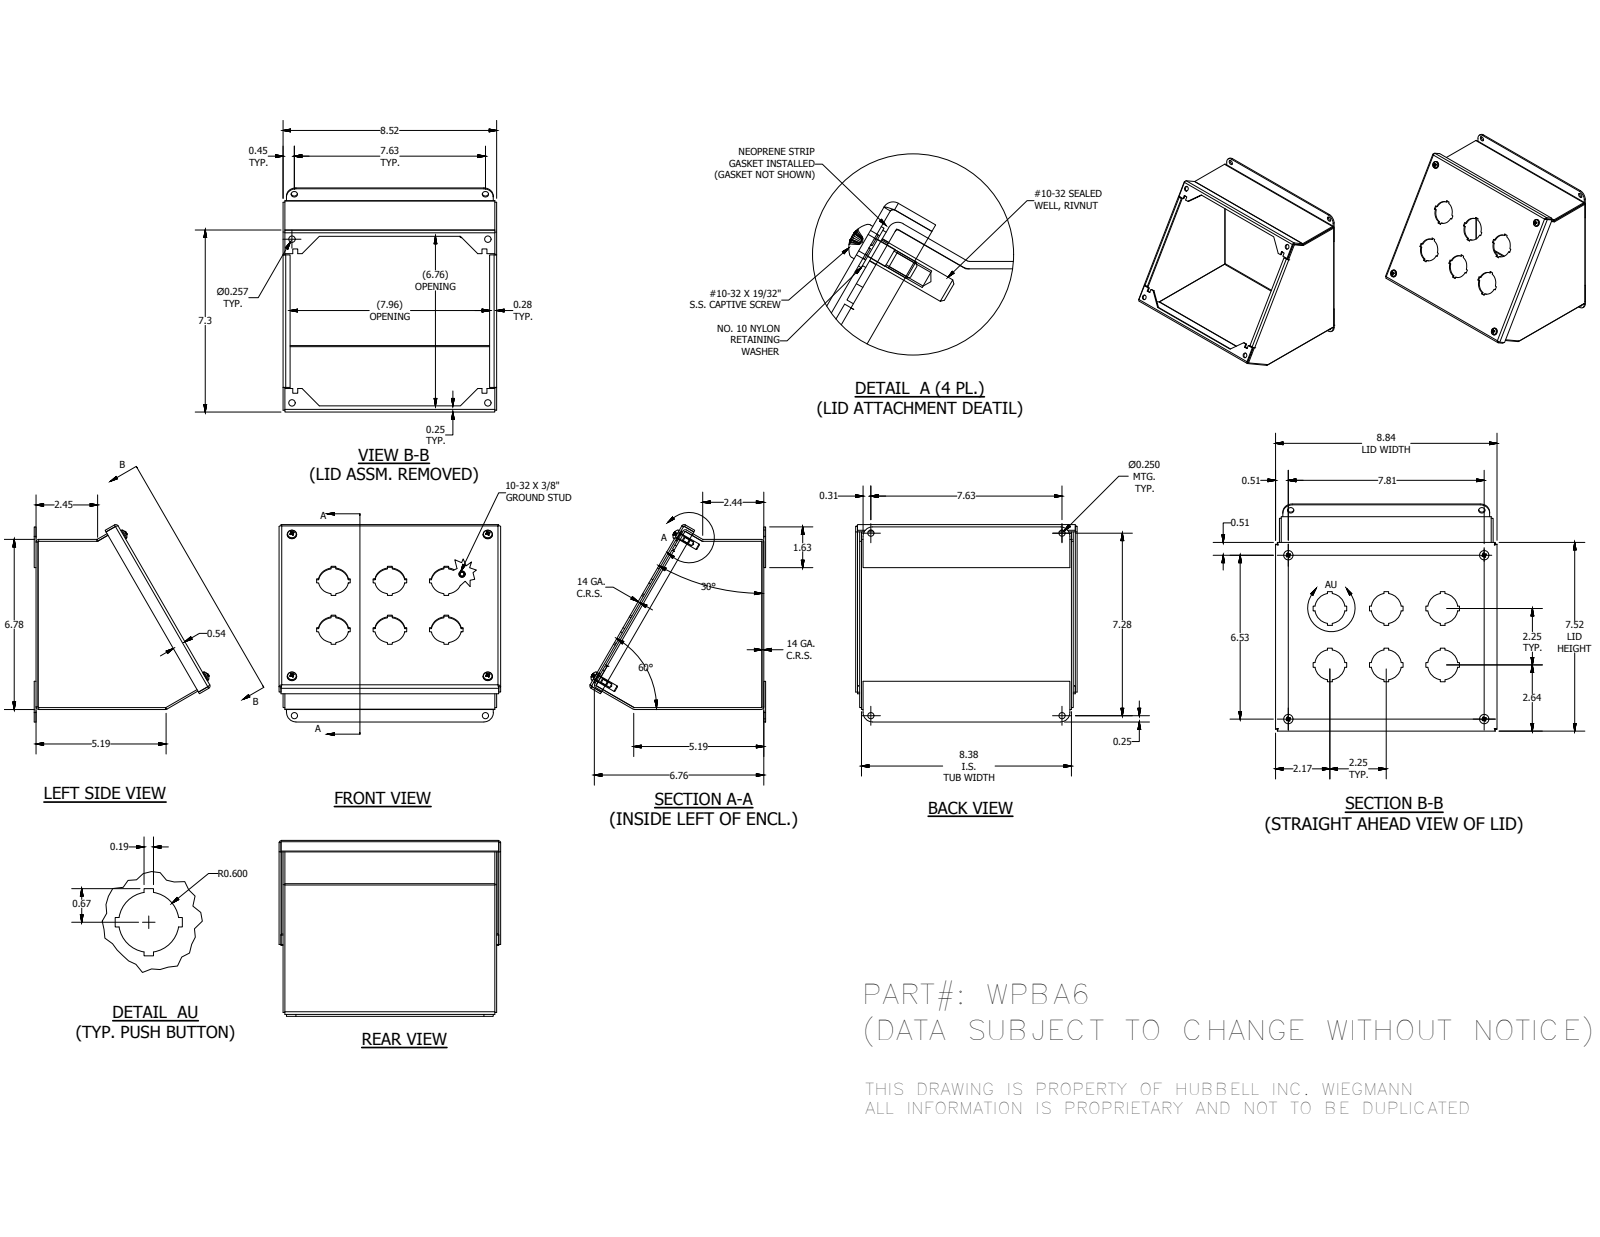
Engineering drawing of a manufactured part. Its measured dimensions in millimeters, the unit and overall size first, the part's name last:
Units: millimetres
Overall size (bounding box): 224.46 × 199.98 × 178.2
Round holes (diameter × count): ⌀30.48 ×6, ⌀3.96 ×4, ⌀4.98 ×4, ⌀6.35 ×4, ⌀6.53 ×4, ⌀7.06 ×4, ⌀7.14 ×4
Round bosses / shafts (diameter × count): ⌀4.83 ×5, ⌀11.51 ×4, ⌀10.31 ×4, ⌀9.47 ×4, ⌀6.3 ×4, ⌀6.35 ×1
Partial cylindrical surfaces — rounded edges, fillets, slot ends (radius × count): R0.79 ×12, R2.67 ×12, R2.27 ×4, R9.53 ×4
Main face-to-face distances: 1.88, 214.6, 170.33, 212.72, 216.48, 3.76, 168.45, 172.21, 3.66, 3.04
Hole centre spacings: 57.15, 68.42, 80.82, 118.8, 165.41, 57.14, 165.07, 165.91
Volume: 387 674 mm³ · Surface area: 424 587 mm²
Bodies: 19 solids, 576 faces (363 planar, 114 cylindrical, 99 other)
Part name (STEP PRODUCT): WPBA6BKP; WPBA2ROWEWPR; WPBA2ROWEWPL; 34984 (+6 more)
STEP written by: Autodesk Inventor 2014 (AUTOMOTIVE_DESIGN)
